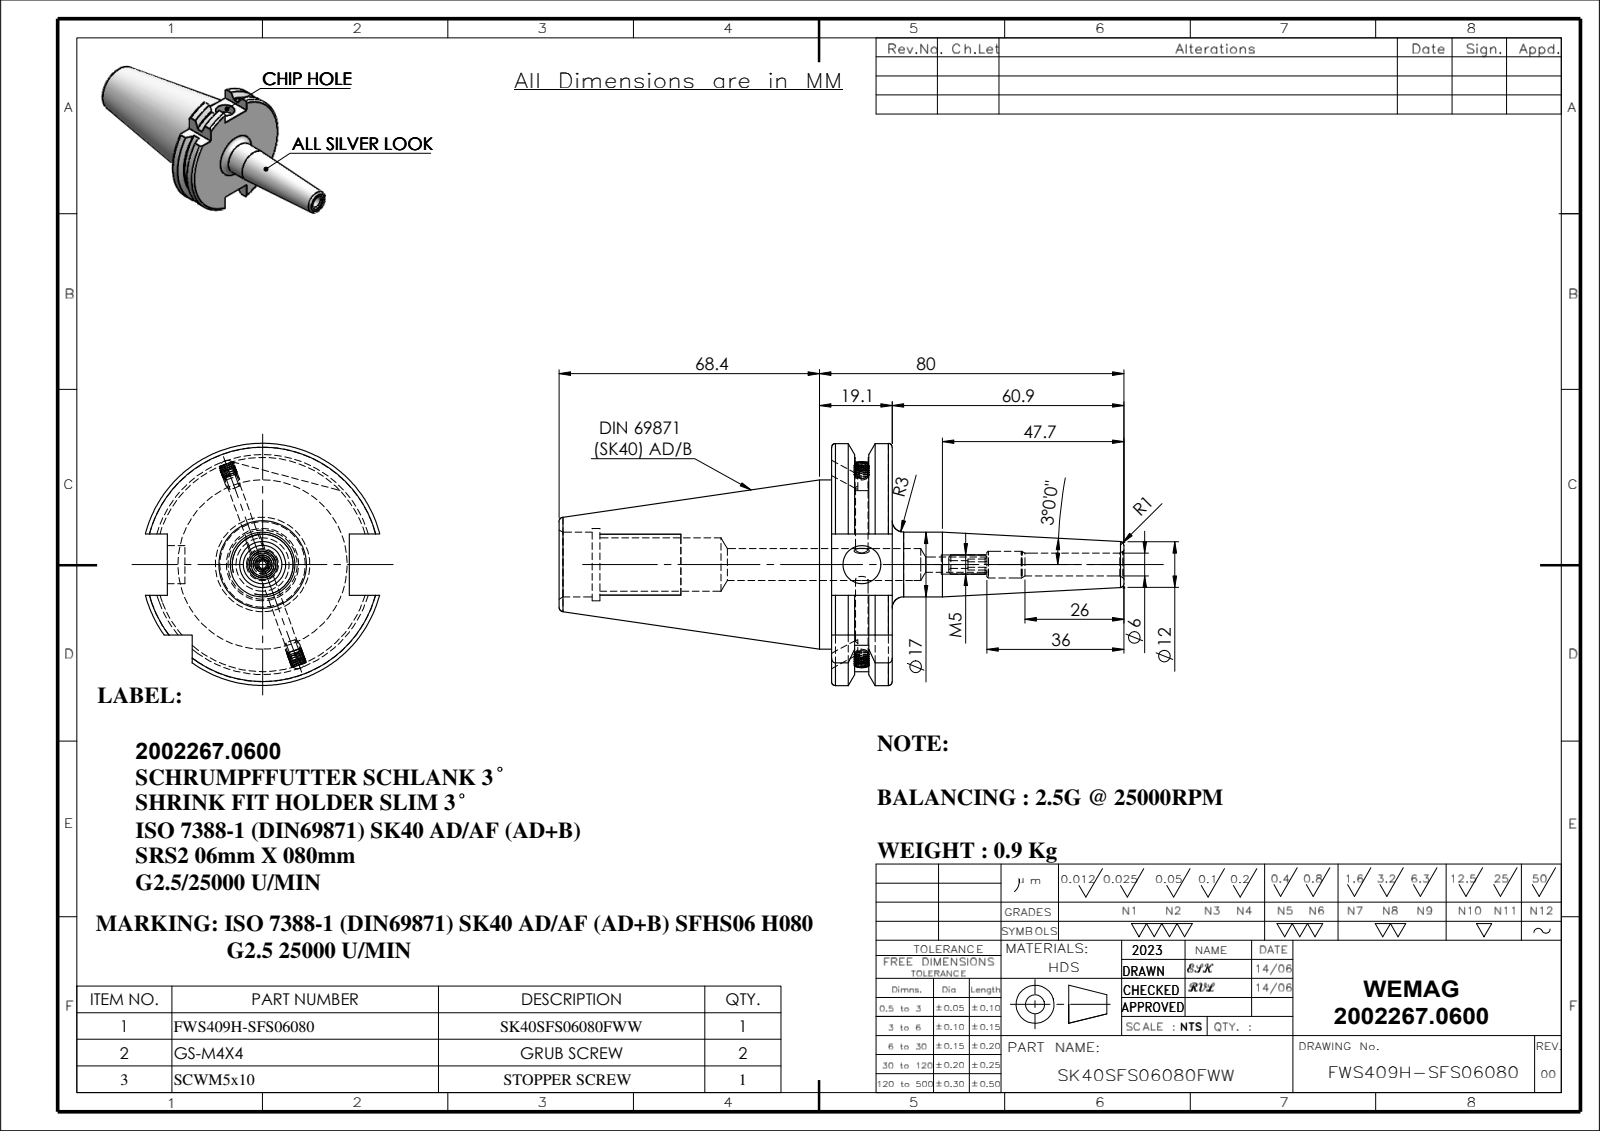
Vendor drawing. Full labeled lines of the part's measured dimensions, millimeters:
Part name (STEP PRODUCT): SK40SFS06080FWW; SCWM5X10; 91406-SRS06080; GS-M4X4_DIN 913 - M4 x 4-N
STEP written by: SolidWorks 2018 (CONFIG_CONTROL_DESIGN)
Units: millimetres
Bodies: 4 solids, 230 faces (62 planar, 60 cylindrical, 108 other)
Overall size (bounding box): 148.4 × 63.55 × 61.48
Volume: 112 102 mm³ · Surface area: 25 034 mm²
Round holes (diameter × count): ⌀2 ×1, ⌀3.3 ×1, ⌀4 ×1, ⌀6 ×1, ⌀7 ×1, ⌀8.4 ×1, ⌀10 ×1, ⌀14 ×1, ⌀17 ×1, ⌀19 ×1
Round bosses / shafts (diameter × count): ⌀4 ×2, ⌀44.45 ×1, ⌀5 ×1
Partial cylindrical surfaces — rounded edges, fillets, slot ends (radius × count): R28.12 ×1, R31.77 ×1
Main face-to-face distances: 15.9, 16.1, 47.8, 60.9, 76.8, 71.6, 87.5, 10.7, 77.63, 66.93
